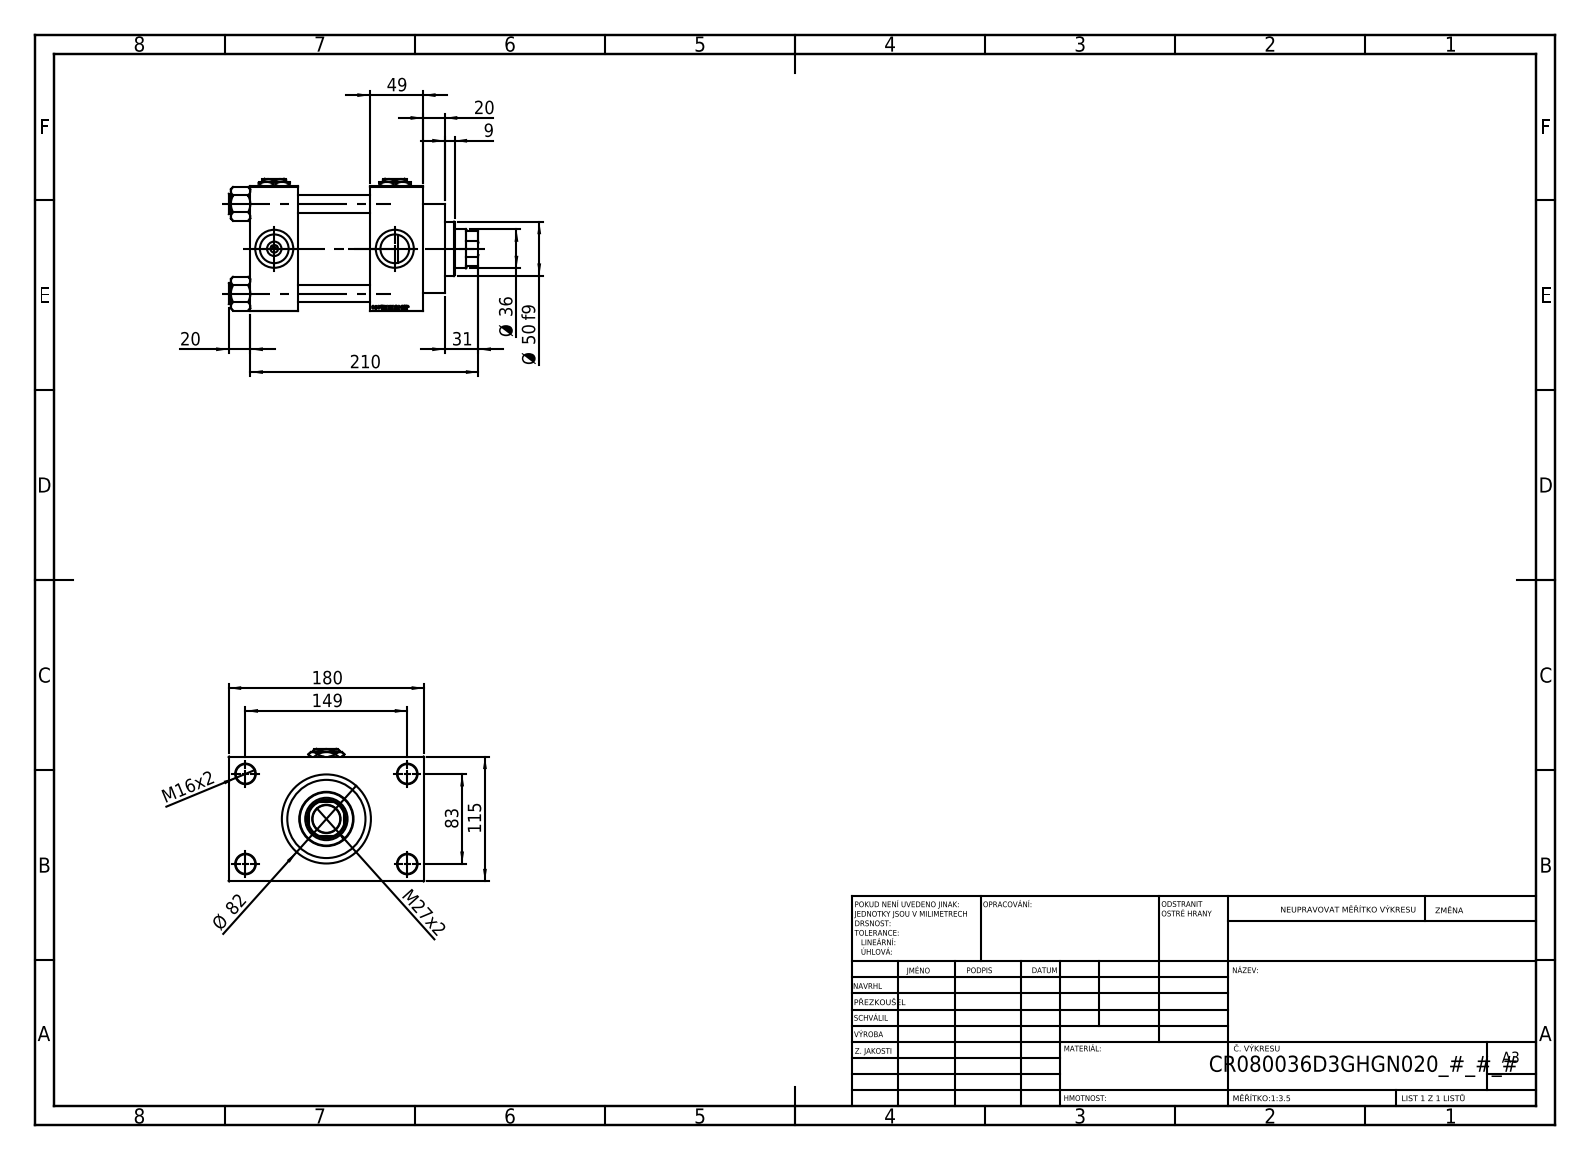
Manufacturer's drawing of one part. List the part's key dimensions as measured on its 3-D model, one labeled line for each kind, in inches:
Part name (STEP PRODUCT): NUT_M5_D; V215CR_VCP_D; V215CR_D_Body; V215_VC_A (+2 more)
STEP written by: SolidWorks 2019 (CONFIG_CONTROL_DESIGN)
Units: inches
Bodies: 13 solids, 1252 faces (593 planar, 99 cylindrical, 560 other)
Overall size (bounding box): 9.055 × 7.087 × 4.803
Volume: 120 in³ · Surface area: 470.1 in²
Round holes (diameter × count): ⌀0.63 ×4, ⌀0.709 ×4, ⌀1.041 ×4, ⌀1.378 ×4, ⌀0.276 ×3, ⌀1.004 ×1, ⌀1.417 ×1, ⌀1.535 ×1, ⌀2.402 ×1, ⌀2.835 ×1, ⌀3.15 ×1
Round bosses / shafts (diameter × count): ⌀0.748 ×4, ⌀3.386 ×1, ⌀3.228 ×1, ⌀1.969 ×1
Partial cylindrical surfaces — rounded edges, fillets, slot ends (radius × count): R0.689 ×1
Main face-to-face distances: 4.528, 2.598, 4.331, 1.929, 1.732, 6.26, 1.28, 5.807, 0.787, 2.717
Hole centre spacings: 1.305, 2.302, 3.256, 3.357, 3.513, 4.561, 5.607, 3.268
